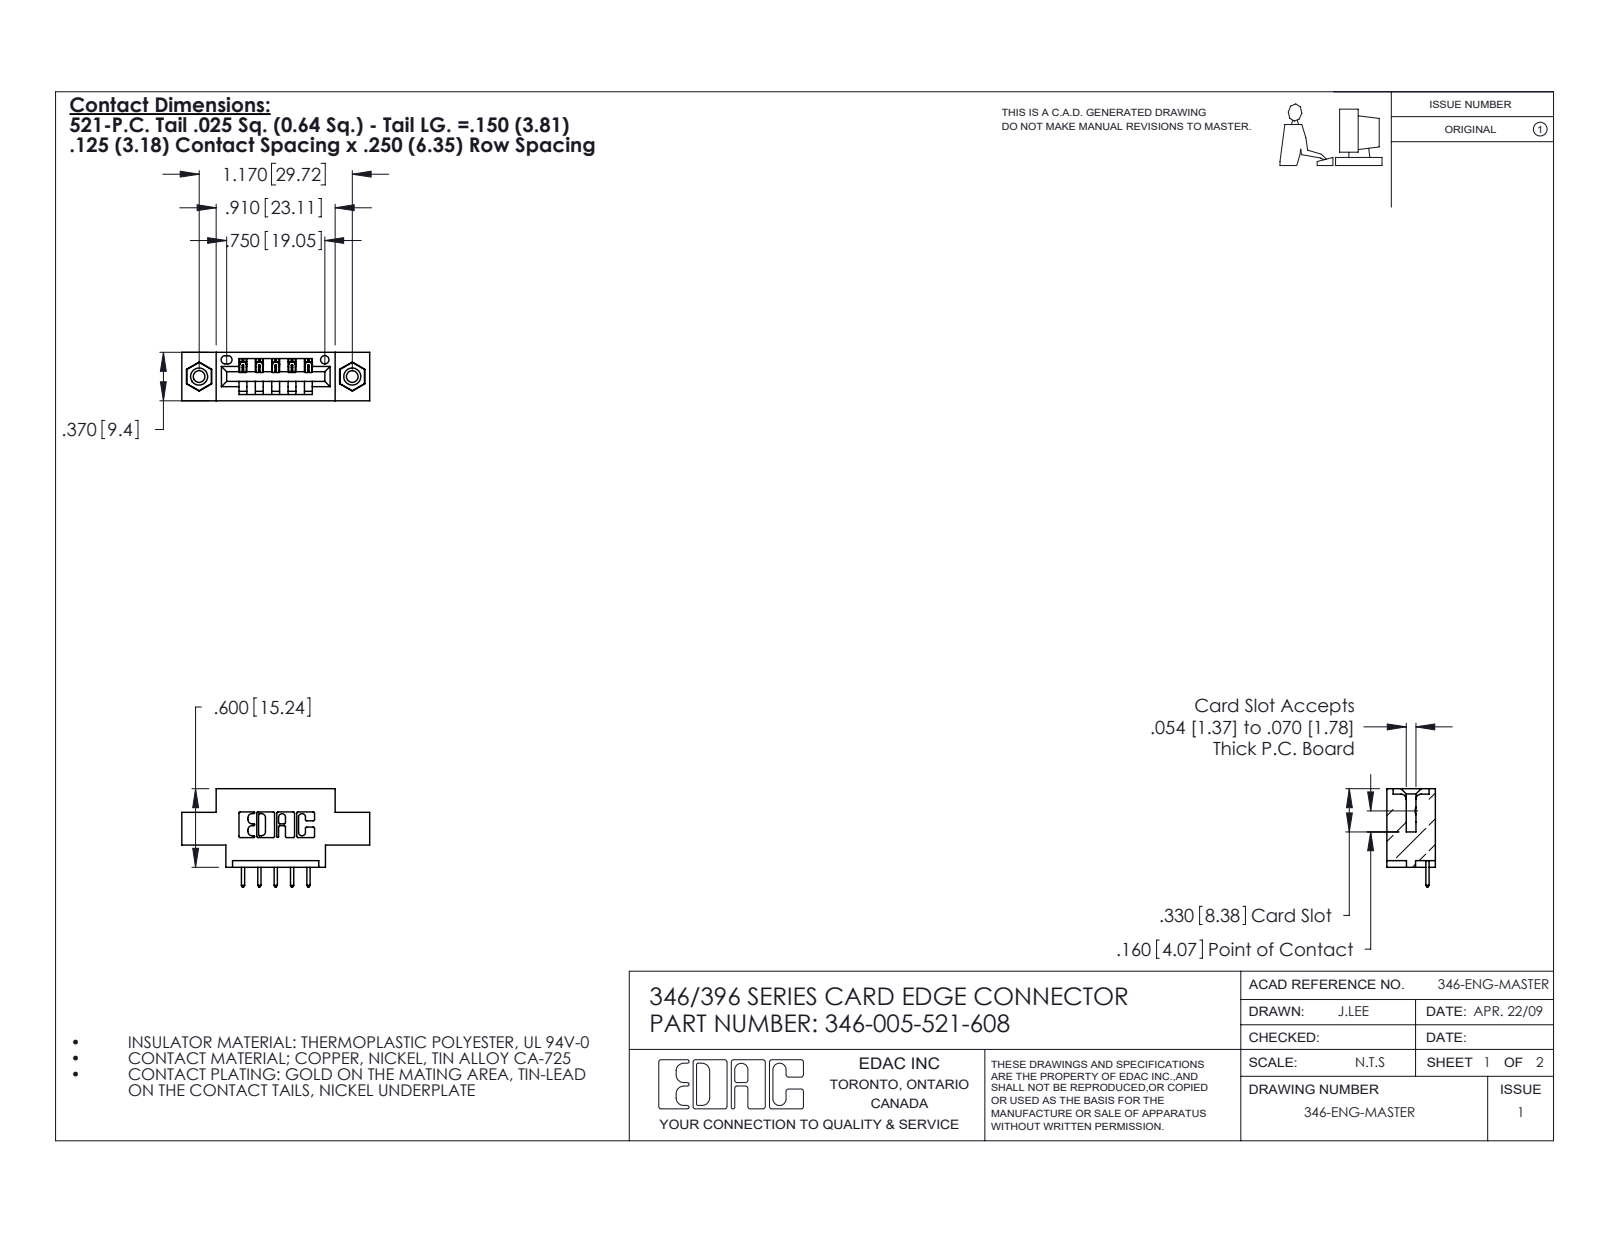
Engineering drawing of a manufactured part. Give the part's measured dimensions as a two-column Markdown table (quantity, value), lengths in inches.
| quantity | value |
| --- | --- |
| part name | 345-292-001_345-293-121; 346-005-521-608; 346 Part_0.170 Offset - 0.156 Dia-TI; 345-250-001_345-250-003-102 |
| STEP written by | SolidWorks 2020 (CONFIG_CONTROL_DESIGN) |
| units | inches |
| bodies | 8 solids, 476 faces (312 planar, 148 cylindrical, 16 other) |
| overall size | 1.435 × 0.75 × 0.37 |
| volume | 0.187 in³ |
| surface area | 5.501 in² |
| round holes (diameter × count) | 0.089 × 2, 0.125 × 2, 0.156 × 2, 0.064 × 1 |
| round bosses / shafts (diameter × count) | 0.155 × 2 |
| partial cylindrical surfaces (radius × count) | 0.01 × 22, 0.006 × 10, 0.01 × 10, 0.007 × 6, 0.031 × 6, 0.026 × 3, 0.031 × 2, 0.04 × 2 |
| main face-to-face distances | 0.25, 0.37, 0.048, 0.322, 0.222, 0.148, 0.1, 0.174, 0.55, 0.125 |
| hole center spacings | 0.246, 0.969, 1.17 |
